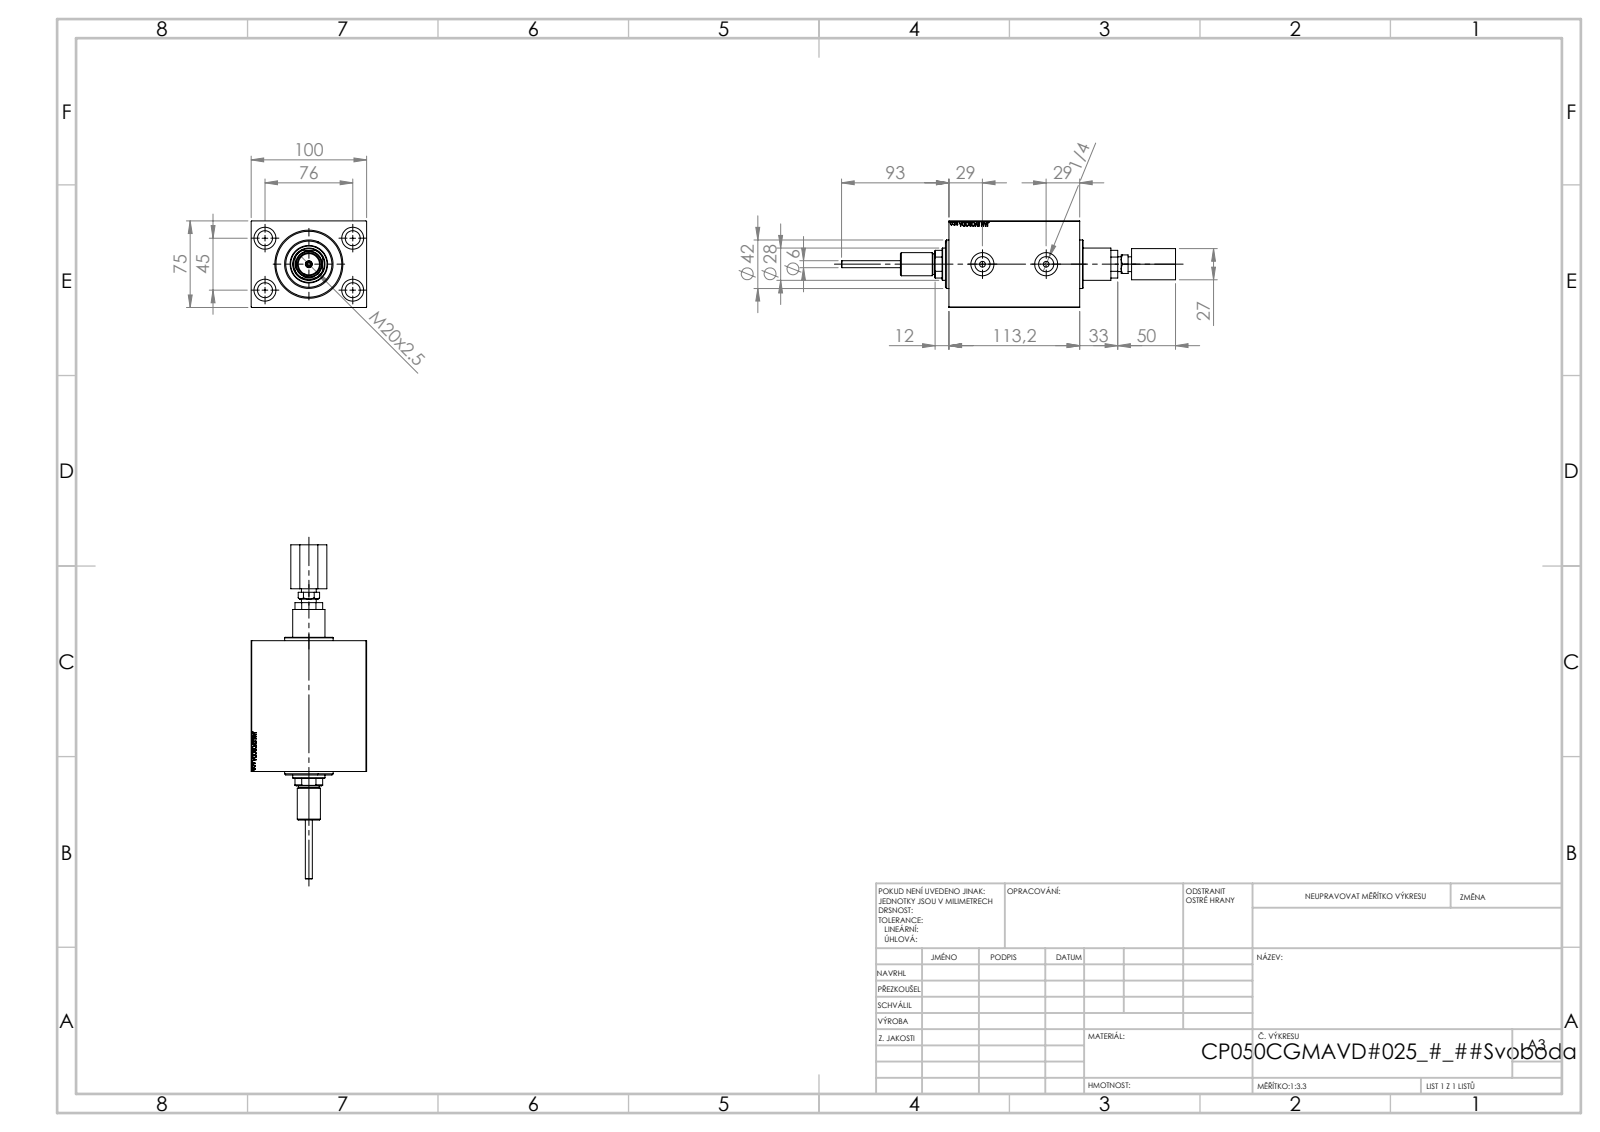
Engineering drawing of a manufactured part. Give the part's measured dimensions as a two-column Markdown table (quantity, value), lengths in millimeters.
| quantity | value |
| --- | --- |
| part name | V450DCP_C_Body; V450DCP_B_RodCooling_ACCESSORIES; V450CP_MALE_METRIC; V450DCP_B_VCP (+1 more) |
| STEP written by | SolidWorks 2019 (CONFIG_CONTROL_DESIGN) |
| units | millimeters |
| bodies | 5 solids, 970 faces (446 planar, 106 cylindrical, 418 other) |
| overall size | 289.2 × 100 × 75 |
| volume | 792 604 mm³ |
| surface area | 145 943 mm² |
| round holes (diameter × count) | 13 × 4, 19 × 4, 4 × 2, 5 × 2, 9.73 × 2, 13.16 × 2, 15 × 2, 20 × 2, 3 × 1, 6 × 1, 18.5 × 1, 28 × 1 |
| round bosses / shafts (diameter × count) | 42 × 1, 20 × 1, 18 × 1, 12.78 × 1 |
| partial cylindrical surfaces (radius × count) | 13.5 × 1 |
| main face-to-face distances | 75, 100, 99.2, 113.2, 14, 13, 1, 112.2, 55, 30 |
| hole center spacings | 44.16, 45, 76, 88.32, 42.55, 55.2 |
